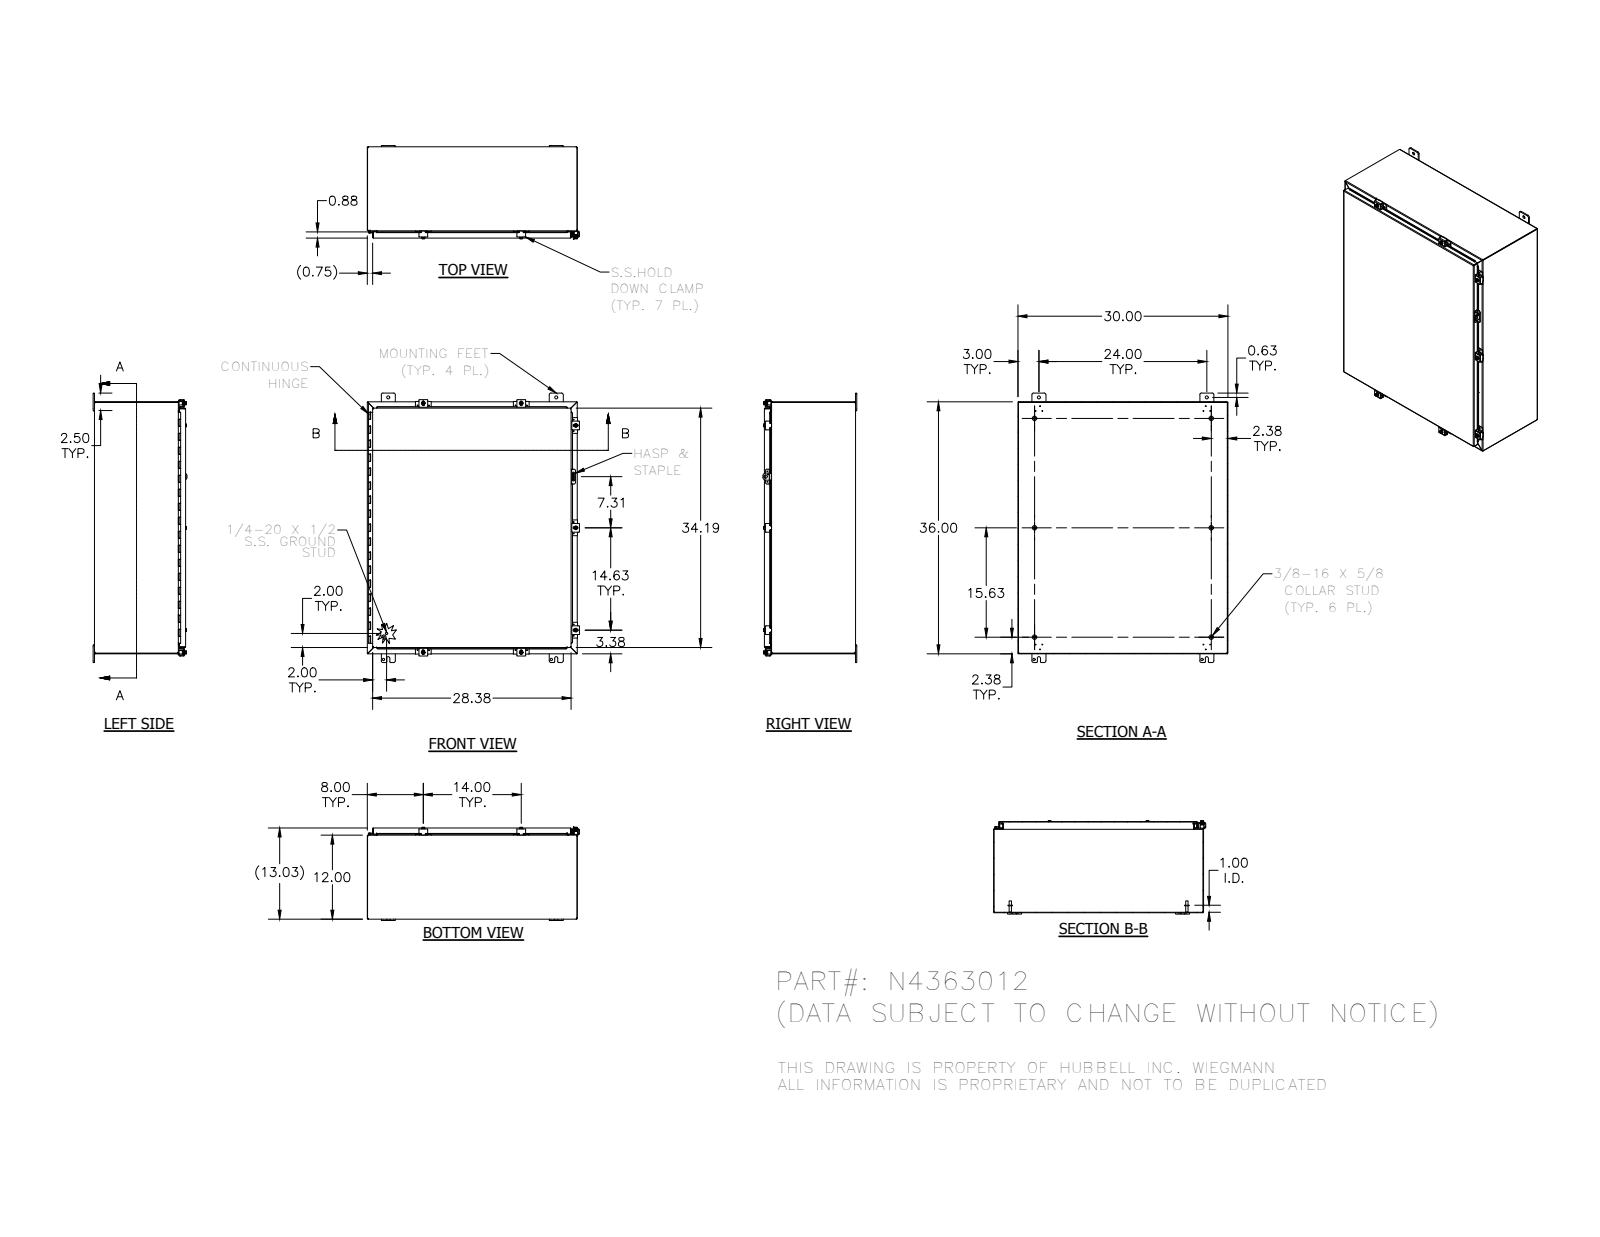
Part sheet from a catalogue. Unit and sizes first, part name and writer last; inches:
Units: inches
Overall size (bounding box): 38.5 × 30.311 × 13.41
Round holes (diameter × count): ⌀0.11 ×17, ⌀0.12 ×12, ⌀0.211 ×7, ⌀0.281 ×7, ⌀0.3 ×7, ⌀0.313 ×4, ⌀0.438 ×4, ⌀0.125 ×1, ⌀0.156 ×1, ⌀0.5 ×1
Round bosses / shafts (diameter × count): ⌀0.25 ×9, ⌀0.52 ×7, ⌀0.5 ×7, ⌀0.35 ×7, ⌀0.625 ×6, ⌀0.33 ×6, ⌀0.115 ×2, ⌀0.337 ×1
Partial cylindrical surfaces — rounded edges, fillets, slot ends (radius × count): R0.03 ×83, R0.062 ×41, R0.125 ×37, R0.25 ×33, R0.031 ×23, R0.105 ×23, R0.063 ×14, R0.141 ×14
Main face-to-face distances: 0.074, 12.959, 12.885, 13.033, 29.926, 35.926, 29.852, 30, 35.852, 36
Hole centre spacings: 24, 0.876, 0.759, 0.94, 0.969, 1.995, 23.367, 24.335
Volume: 323.1 in³ · Surface area: 8 526 in²
Bodies: 54 solids, 2404 faces (930 planar, 1087 cylindrical, 387 other)
Part name (STEP PRODUCT): 38846_1; 32911_1; 388116_1; HFW30825-4_1 (+8 more)
STEP written by: SolidWorks 2014 (AUTOMOTIVE_DESIGN)
